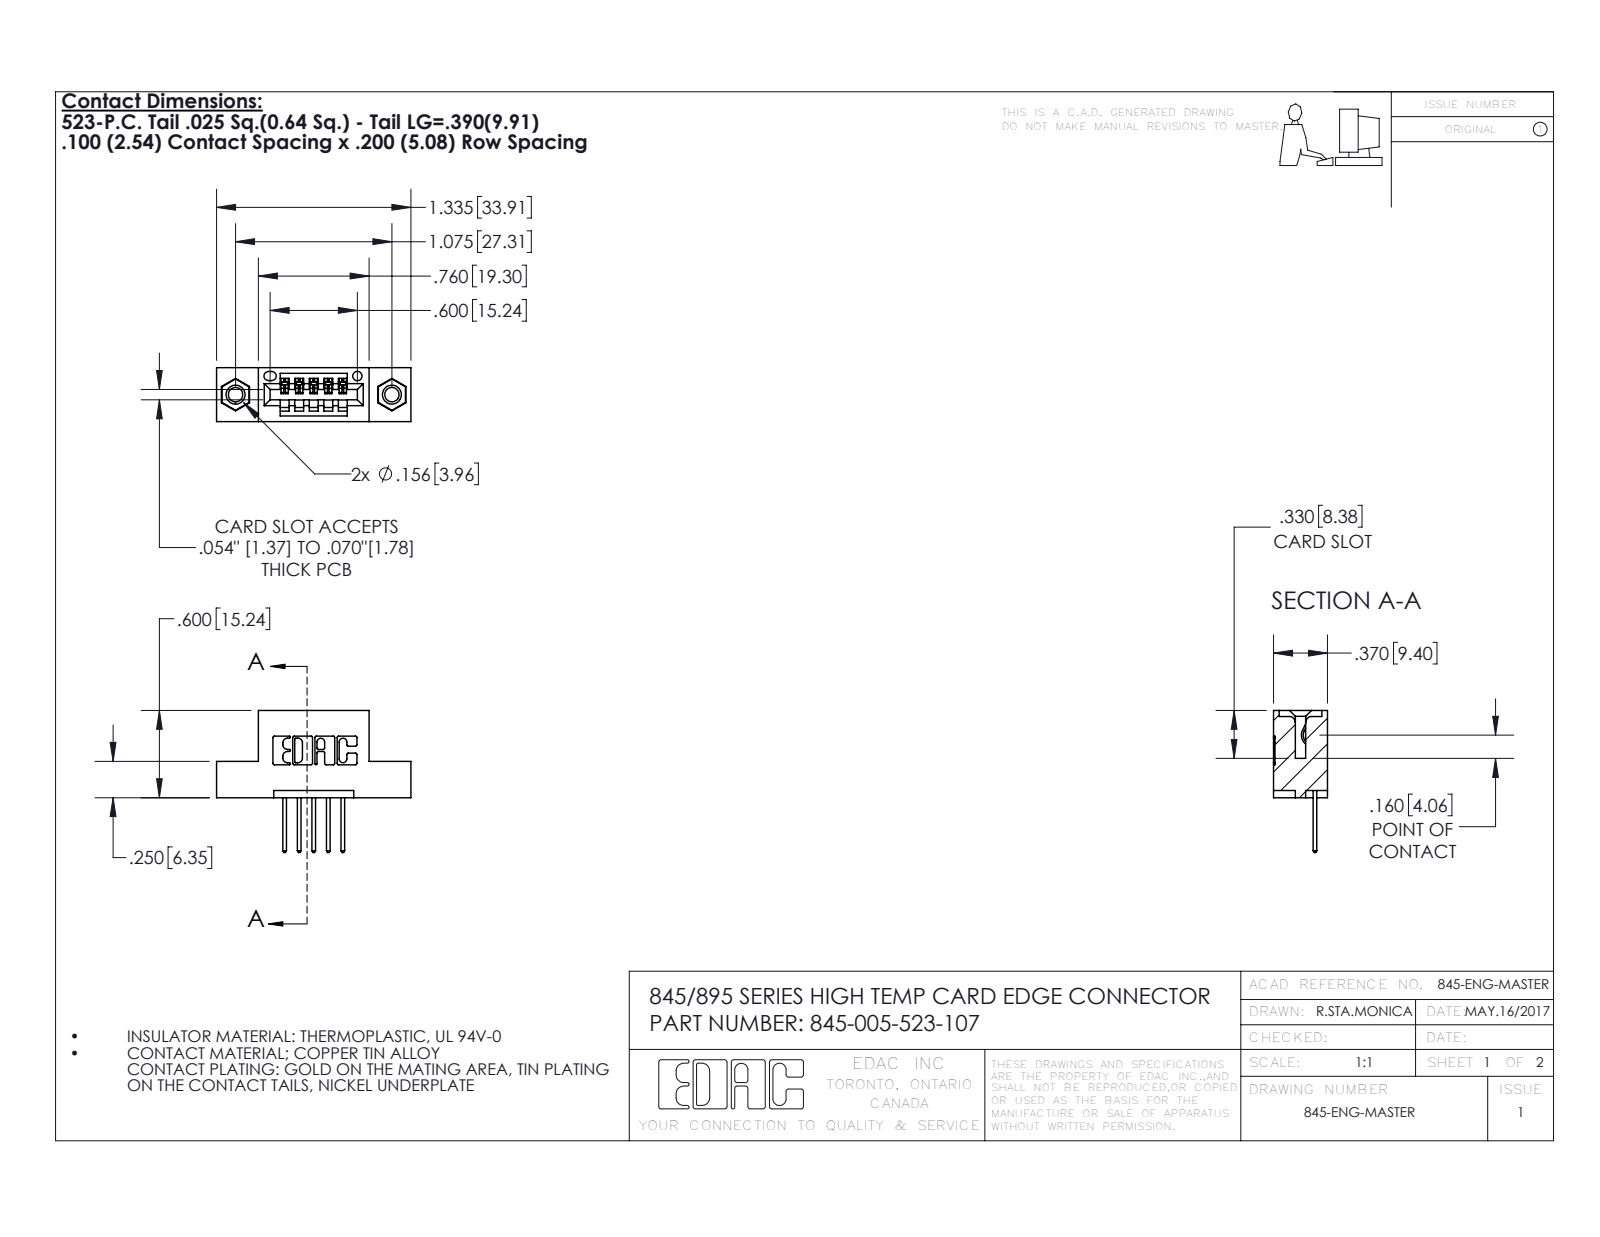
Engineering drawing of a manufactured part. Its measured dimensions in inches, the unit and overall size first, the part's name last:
Units: inches
Overall size (bounding box): 1.335 × 0.977 × 0.37
Round holes (diameter × count): ⌀0.098 ×2, ⌀0.125 ×2, ⌀0.156 ×2, ⌀0.064 ×1
Round bosses / shafts (diameter × count): ⌀0.155 ×2
Partial cylindrical surfaces — rounded edges, fillets, slot ends (radius × count): R0.01 ×22, R0.006 ×10, R0.01 ×10, R0.007 ×6, R0.031 ×6, R0.026 ×3, R0.031 ×2, R0.04 ×2
Main face-to-face distances: 0.2, 0.37, 0.072, 0.298, 0.1, 0.025, 0.098, 0.272, 0.35, 0.25
Hole centre spacings: 0.27, 0.847, 1.075
Volume: 0.177 in³ · Surface area: 5.257 in²
Bodies: 8 solids, 476 faces (312 planar, 148 cylindrical, 16 other)
Part name (STEP PRODUCT): 345-292-001_345-293-123; 345-005-523-107; 345 Part_Flush Mounting Lugs - 0.156 Dia-TI; 345-250-001_345-250-005-103
STEP written by: SolidWorks 2016 (CONFIG_CONTROL_DESIGN)
